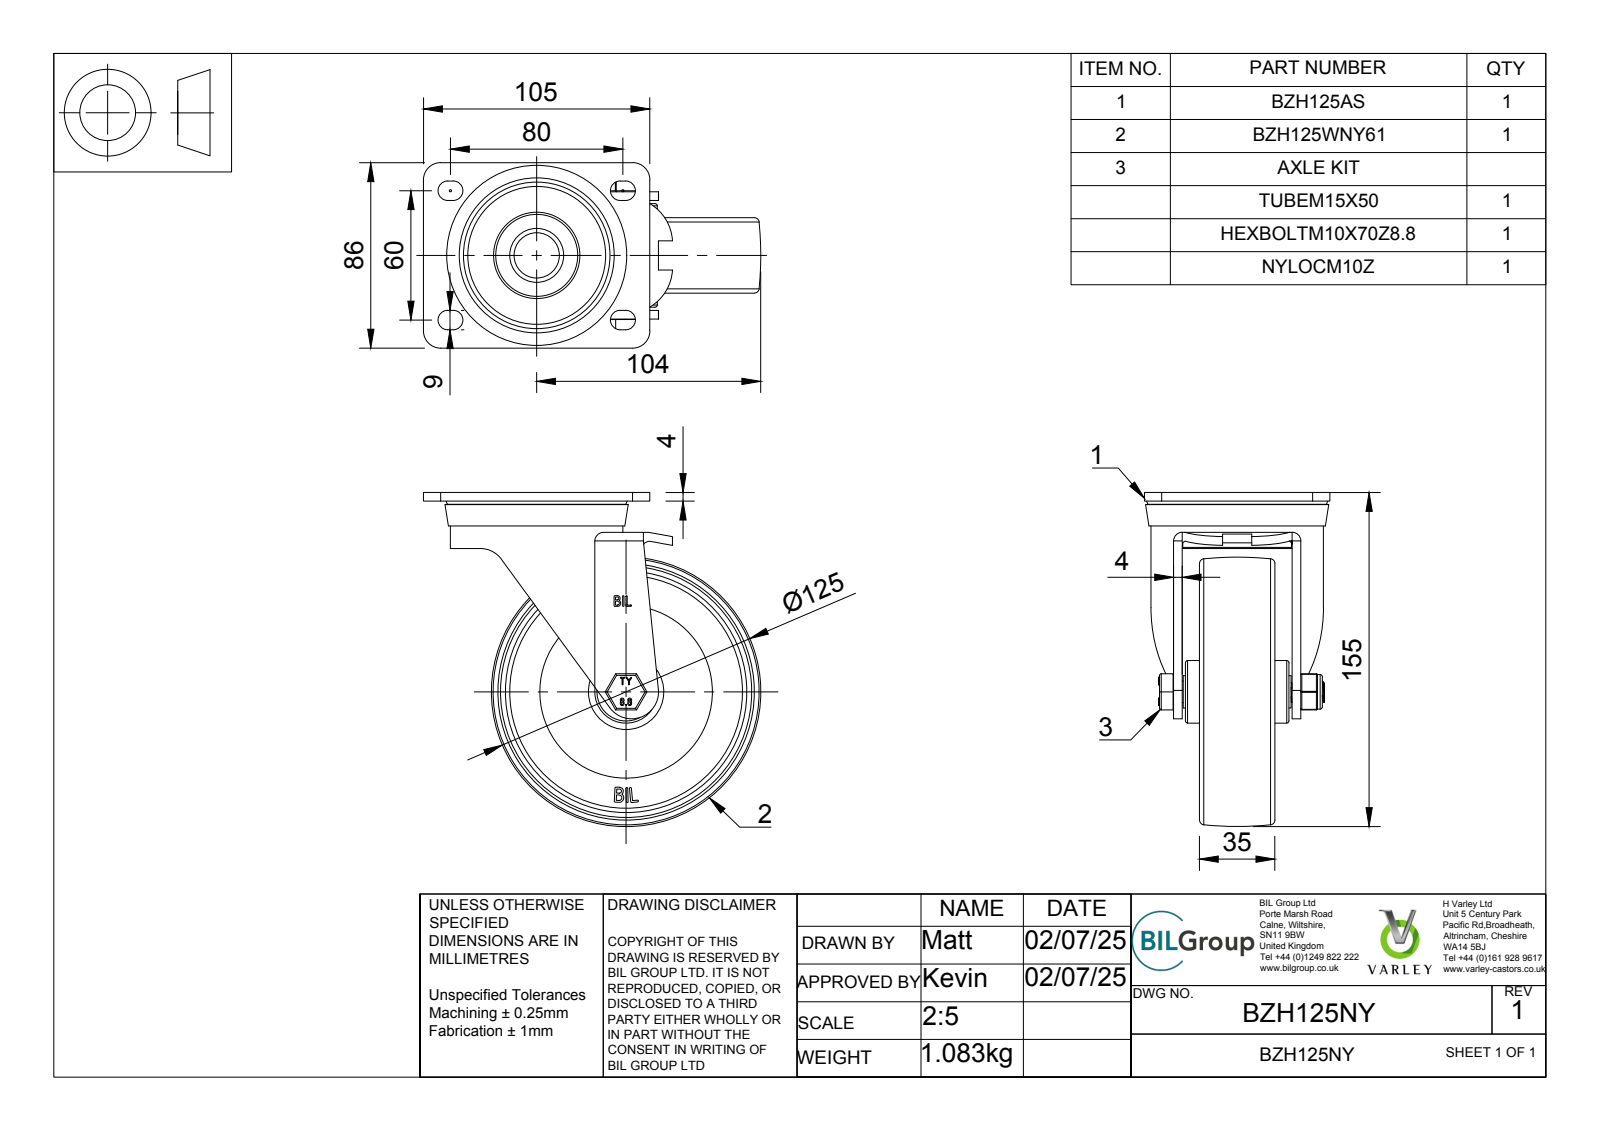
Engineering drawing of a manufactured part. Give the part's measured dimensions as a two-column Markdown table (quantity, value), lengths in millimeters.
| quantity | value |
| --- | --- |
| part name | BZH125NY v3; BZH125AS - 2 v2; ZINC PLATED, PRESSED STEEL TOP PLATE; ZINC PLATED, PRESSED STEEL FORKS (+8 more) |
| STEP written by | Autodesk Translation Framework v14.10.0.0 (AUTOMOTIVE_DESIGN) |
| units | millimeters |
| bodies | 8 solids, 514 faces (251 planar, 115 cylindrical, 148 other) |
| overall size | 156.5 × 155 × 86 |
| volume | 325 288 mm³ |
| surface area | 124 943 mm² |
| round holes (diameter × count) | 10 × 1, 10.2 × 1, 10.5 × 1, 12 × 1, 15.1 × 1, 25 × 1, 32 × 1, 72 × 1, 112 × 1 |
| round bosses / shafts (diameter × count) | 80 × 1, 62 × 1, 50.5 × 1, 31 × 1, 29 × 1, 20 × 1, 16 × 1, 15 × 1 |
| partial cylindrical surfaces (radius × count) | 0.5 × 18, 4.5 × 8, 0.75 × 6, 2 × 4, 8 × 4, 4 × 2, 21.52 × 2, 12 × 1 |
| main face-to-face distances | 4, 7, 7.5, 22, 26, 33, 29, 55, 11.5, 6.5 |
